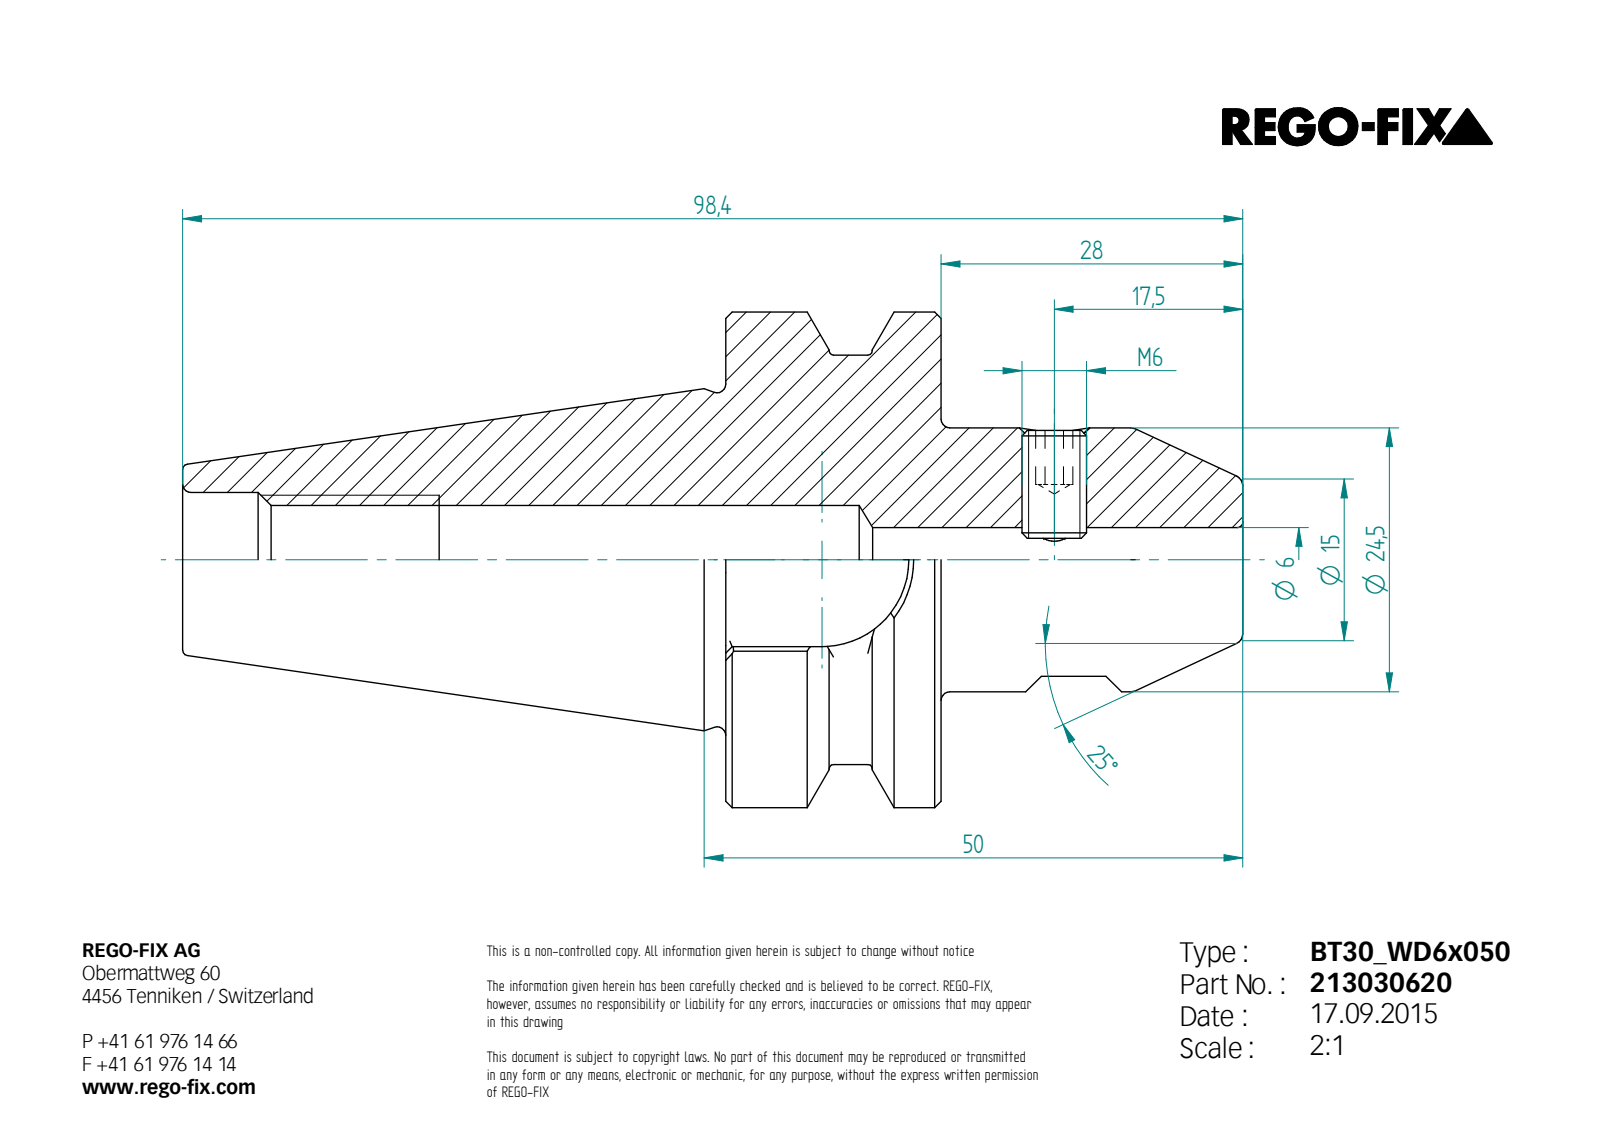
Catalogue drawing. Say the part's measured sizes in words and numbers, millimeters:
Its 3-D file was written by "Unknown (AUTOMOTIVE_DESIGN)". It is 2 solids with 104 faces: 47 planar, 22 cylindrical and 35 other. Overall it measures 98.4 by 46 by 46 millimeters. Its volume is 58 177 cubic millimeters and its surface area 14 810 square millimeters. Round holes: 1 of diameter 4.92, 1 of diameter 6, 1 of diameter 10.11, 1 of diameter 12.5. Round bosses or shafts: 1 of diameter 46, 1 of diameter 24.5, 1 of diameter 6. Partial cylindrical surfaces (rounded edges, fillets, slot ends): 8 of radius 0.5, 1 of radius 8.05, 1 of radius 19. The main face-to-face distances are 20, 32.5, 48, 28, 16.1, 2.75, 18.85, 50.4, 70.4, 98.4.
